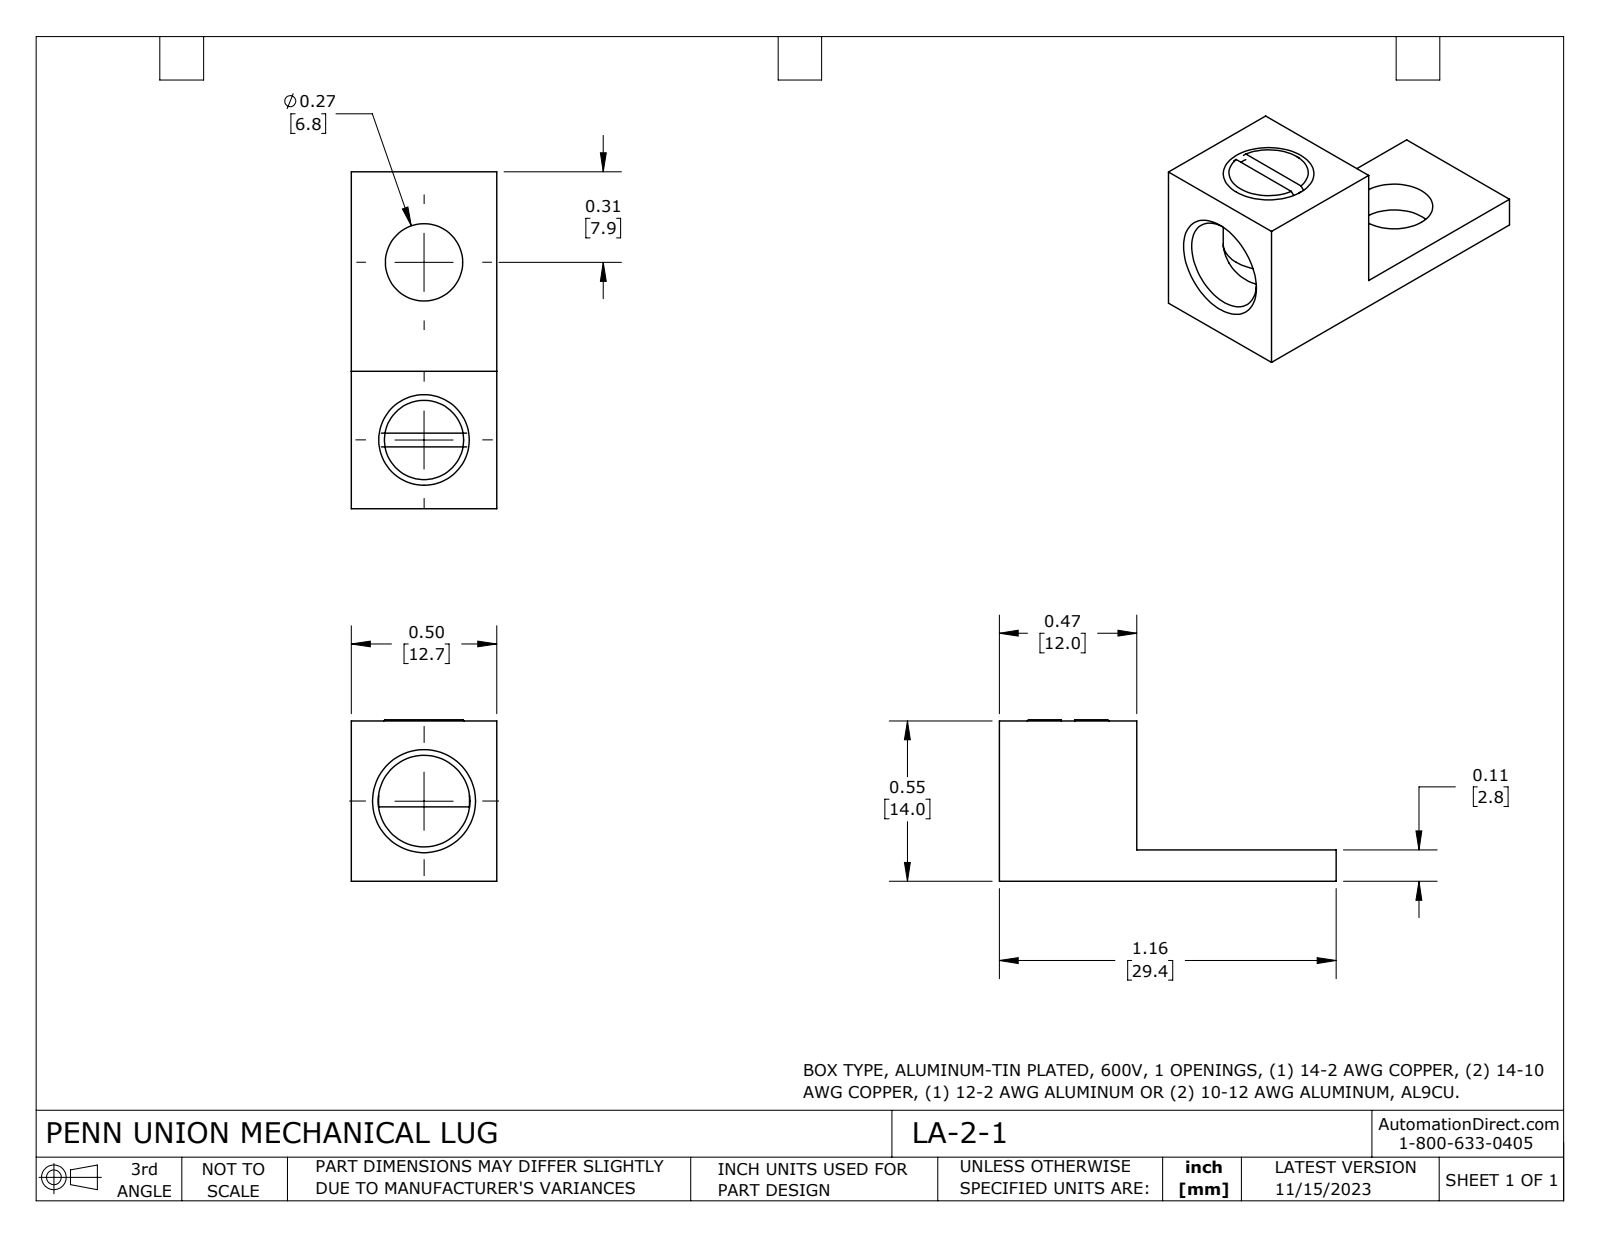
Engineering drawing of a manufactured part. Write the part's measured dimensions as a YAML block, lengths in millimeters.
part_name: "LA-2-1"
step_written_by: "SolidWorks 2023 (CONFIG_CONTROL_DESIGN)"
units: millimeters
bodies: {solids: 2, faces: 30, planar: 13, cylindrical: 8, other: 9}
overall_size: [29.4, 14.1, 12.7]
volume: 2360
surface_area: 2072
round_holes:
  - {diameter: 6.8, count: 1}
  - {diameter: 6.9, count: 1}
  - {diameter: 8, count: 1}
round_bosses_or_shafts:
  - {diameter: 8, count: 1}
face_to_face_distances: [12.7, 2.7, 14, 11.3, 12, 5.4, 6.6, 29.4, 17.4, 14.1]
hole_center_spacings: [15.5]
